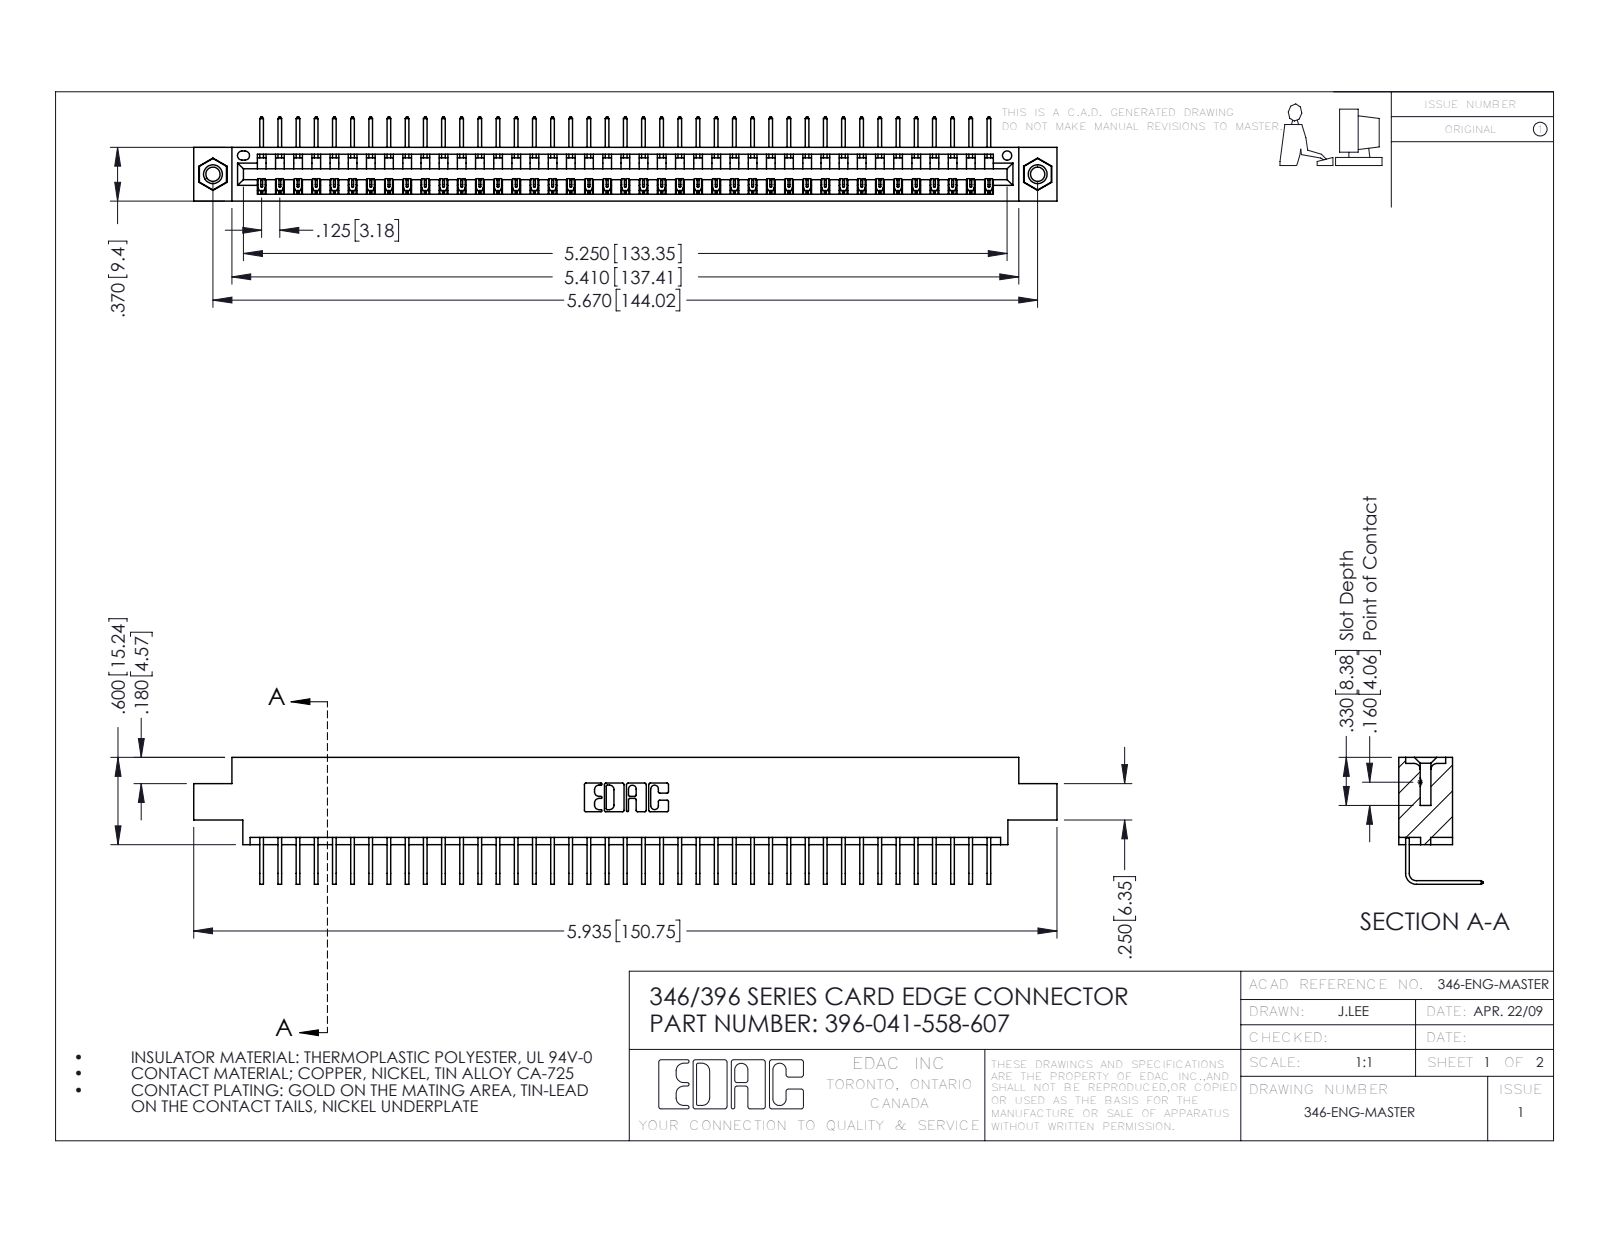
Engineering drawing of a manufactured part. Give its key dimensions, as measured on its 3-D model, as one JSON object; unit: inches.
{"part_name": "345-292-001_558 Tail - 2; 396-041-558-607; 346 Part_0.170 Offset - 0.156 Dia-TI; 345-250-001_345-250-005-103", "step_written_by": "SolidWorks 2016 (CONFIG_CONTROL_DESIGN)", "units": "inches", "bodies": {"solids": 44, "faces": 2646, "planar": 1834, "cylindrical": 796, "other": 16}, "overall_size": [5.935, 0.873, 0.58], "volume_in3": 0.878, "surface_area_in2": 29.43, "round_holes": [[0.098, 2], [0.125, 2], [0.156, 2], [0.064, 1]], "round_bosses_or_shafts": [[0.155, 2]], "partial_cylinders_radius": [[0.006, 82], [0.01, 22], [0.007, 6], [0.031, 6], [0.026, 3], [0.031, 2], [0.04, 2], [0.014, 1]], "face_to_face_distances": [0.322, 0.048, 0.37, 0.25, 0.298, 0.025, 0.072, 0.222, 0.148, 0.1], "hole_center_spacings": [0.246, 5.461, 5.67]}
